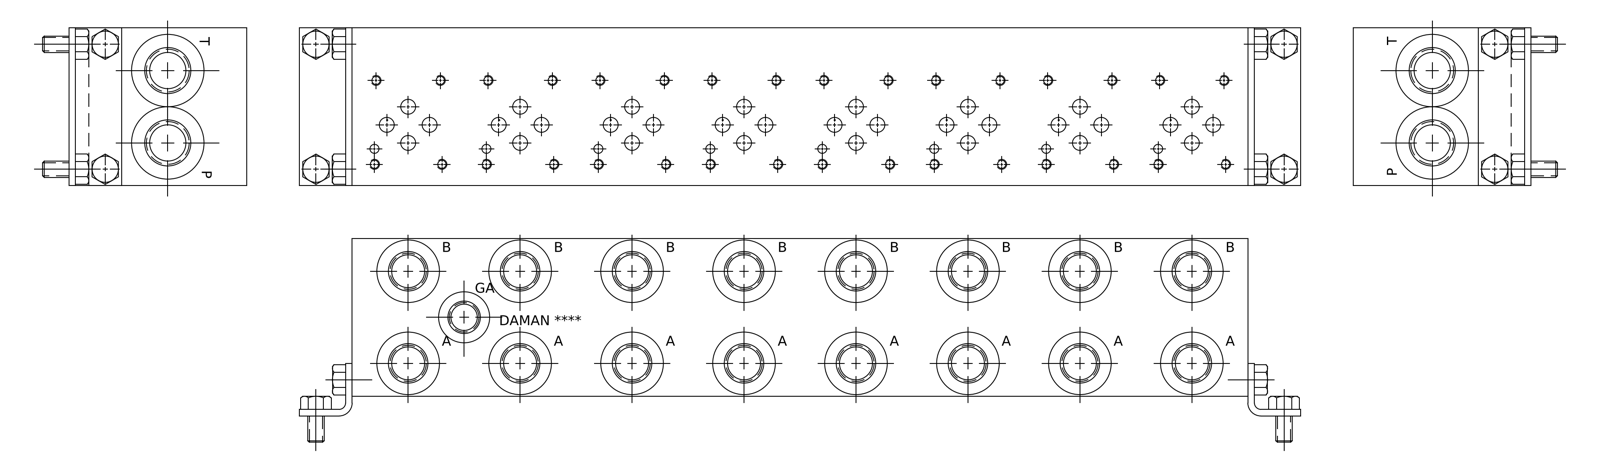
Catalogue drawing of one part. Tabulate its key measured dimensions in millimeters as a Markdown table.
| quantity | value |
| --- | --- |
| part name | Part_AD03P082S_3D |
| STEP written by | Autodesk Inventor 2020 (AUTOMOTIVE_DESIGN) |
| units | millimeters |
| bodies | 1 solid, 1185 faces (553 planar, 217 cylindrical, 415 other) |
| overall size | 431.8 × 76.2 × 76.2 |
| volume | 2 337 000 mm³ |
| surface area | 185 926 mm² |
| round holes (diameter × count) | 3.78 × 32, 4.83 × 32, 7.14 × 24, 15.88 × 16, 17.5 × 16, 19.05 × 16, 19.25 × 16, 30.63 × 16, 3.96 × 8, 6.35 × 8, 6.53 × 2, 7.92 × 2 |
| main face-to-face distances | 76.2, 0.79, 75.41, 431.8, 431.01, 430.22, 15.06, 14.27, 61.14, 0.75 |
| hole center spacings | 107.95, 53.98, 215.9, 53.97, 161.93, 116.74, 161.92, 323.85 |
